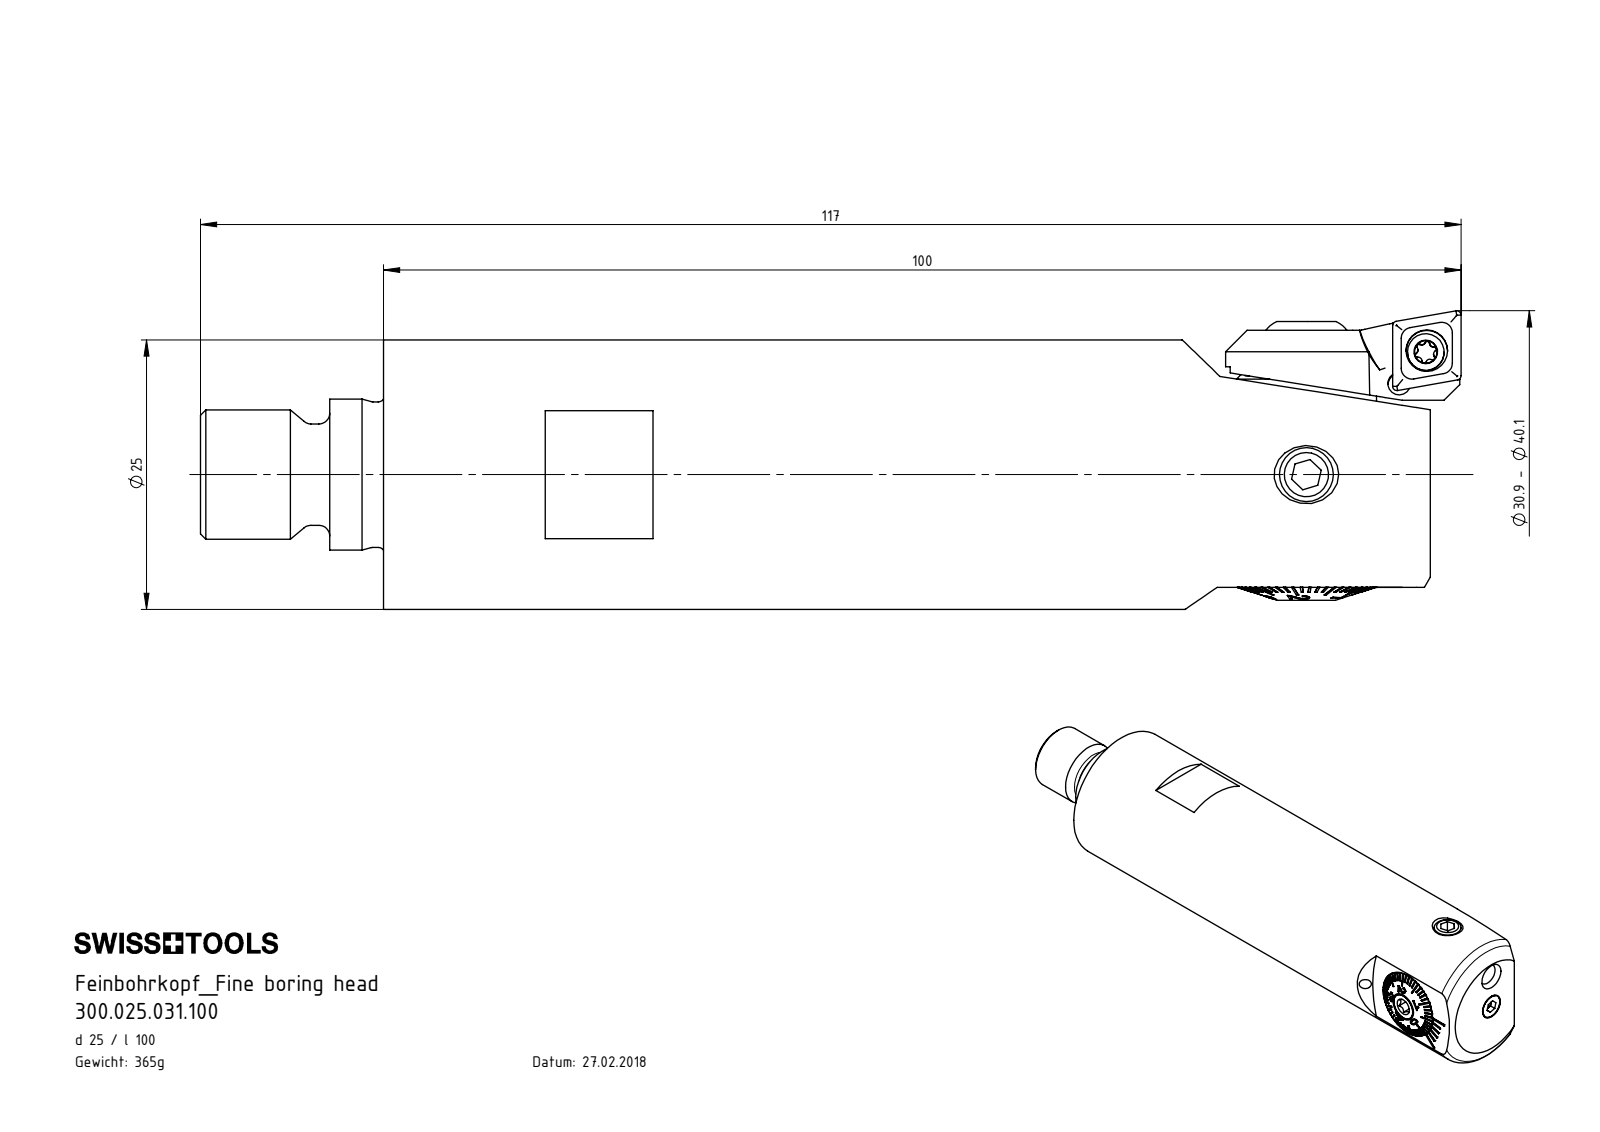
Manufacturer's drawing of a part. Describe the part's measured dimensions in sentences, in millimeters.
The part is named "F25-WCA.001.006_C_fertigbearbeitet; ISO 4026 - M5 x 4; F25-BG1.009.006_A; F25-BG1.012.013 (+8 more)". Its 3-D file was written by "SolidWorks 2017 (CONFIG_CONTROL_DESIGN)". It is 16 solids with 790 faces: 347 planar, 146 cylindrical and 297 other. Overall it measures 117 by 27.7 by 25 millimeters. Its volume is 46 483 cubic millimeters and its surface area 16 811 square millimeters. Round holes: 4 of diameter 2, 2 of diameter 2.05, 2 of diameter 4.2, 2 of diameter 5, 1 of diameter 2.1, 1 of diameter 2.4, 1 of diameter 2.7, 1 of diameter 2.8, 1 of diameter 3, 1 of diameter 3.85, 1 of diameter 5.5, 1 of diameter 6.4. Round bosses or shafts: 2 of diameter 5, 2 of diameter 4.95, 2 of diameter 2.5, 1 of diameter 25, 1 of diameter 14, 1 of diameter 13.5, 1 of diameter 12.98, 1 of diameter 12.85. Partial cylindrical surfaces (rounded edges, fillets, slot ends): 6 of radius 0.21, 5 of radius 0.36, 4 of radius 0.5, 2 of radius 1.32, 1 of radius 0.2, 1 of radius 0.36, 1 of radius 1.05, 1 of radius 1.25. The main face-to-face distances are 97.15, 1.5, 19.95, 3.1, 15.7, 0.8, 19.6, 3.9, 22, 18.8. The hole center spacings are 3.84, 4, 4.08, 6.8, 8.9.
